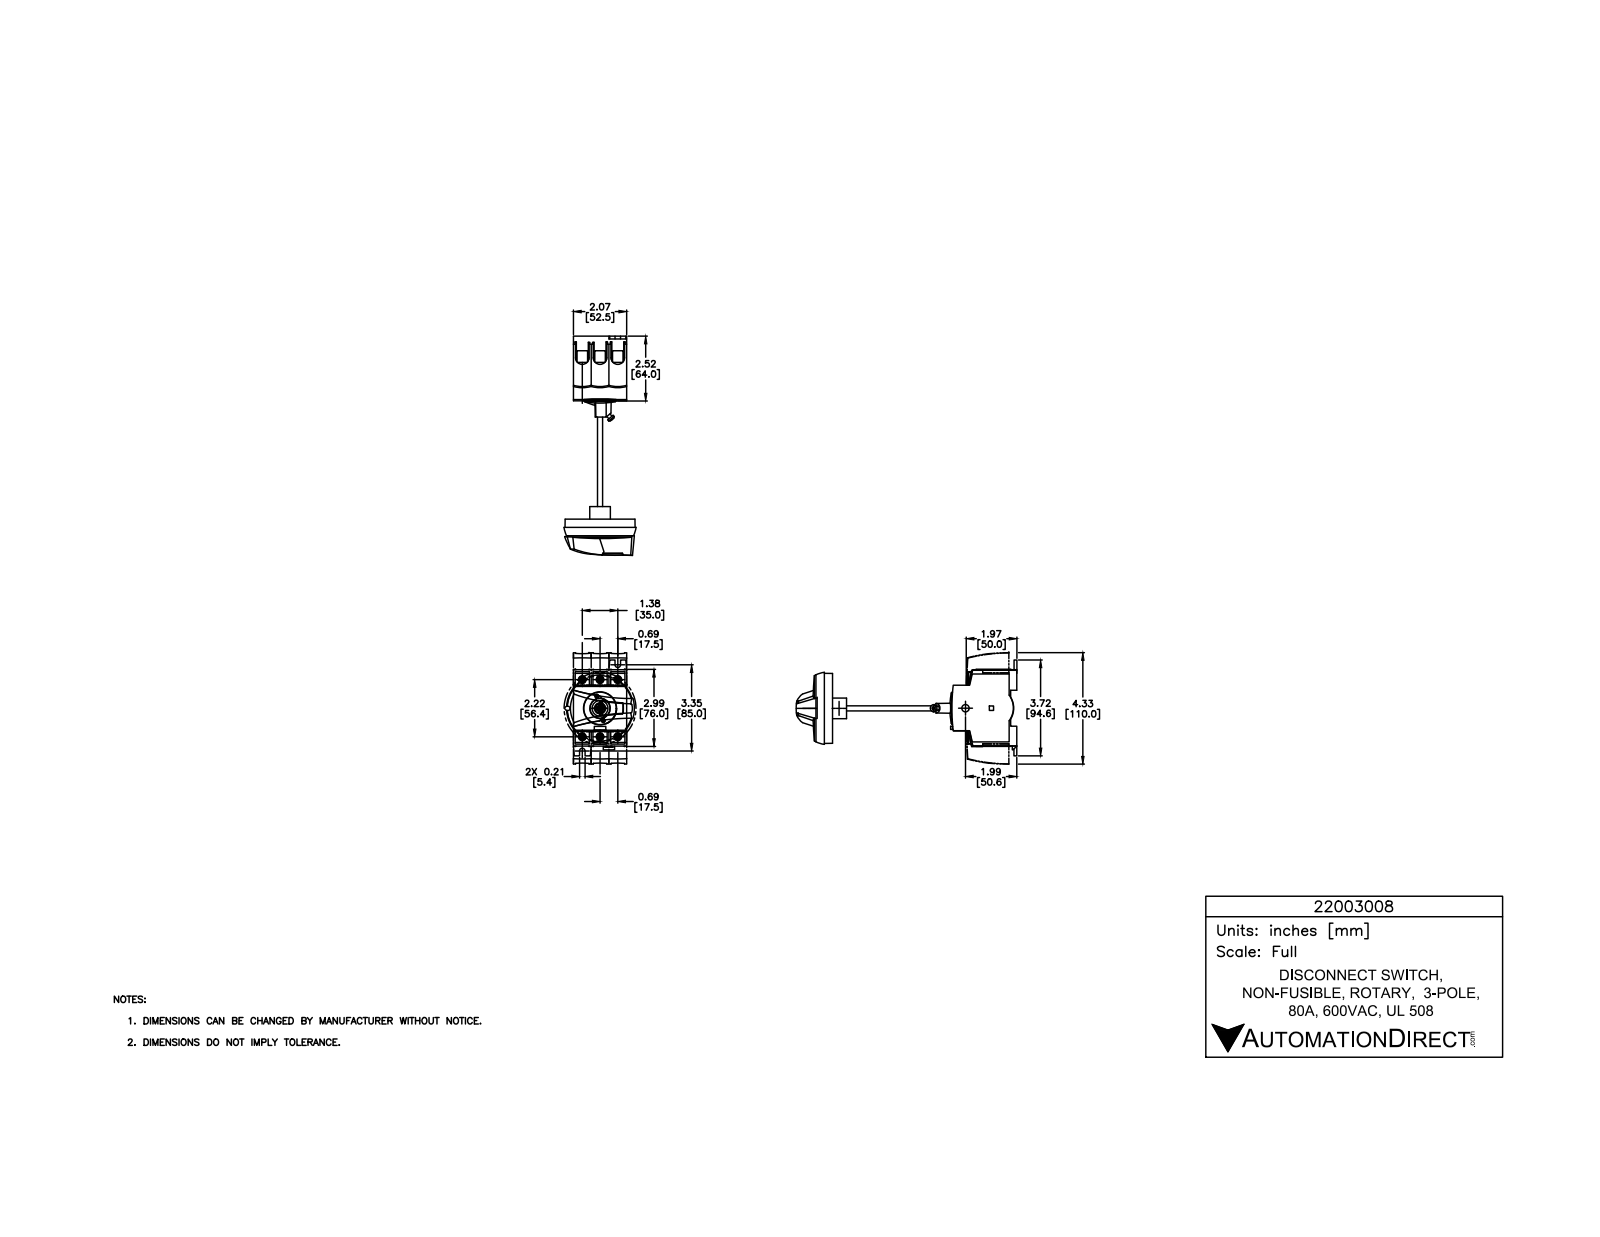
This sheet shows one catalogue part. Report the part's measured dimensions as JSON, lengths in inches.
{"part_name": "22003008-UL", "step_written_by": "SolidWorks 2021 (CONFIG_CONTROL_DESIGN)", "units": "inches", "bodies": {"solids": 1, "faces": 238, "planar": 199, "cylindrical": 39, "other": 0}, "overall_size": [3.724, 2.576, 2.067], "volume_in3": 12.81, "surface_area_in2": 42.15, "round_holes": [[0.26, 6], [0.283, 1], [1.26, 1]], "partial_cylinders_radius": [[1.18, 9], [0.012, 4], [0.106, 2], [0.37, 1], [0.827, 1], [7.862, 1]], "face_to_face_distances": [2.067, 2.969, 2.391, 2.382, 0.61, 0.142, 2.827, 0.587, 2.358, 1.772], "hole_center_spacings": [0.689, 1.307, 2.325, 2.22, 1.11, 1.378, 2.613]}
